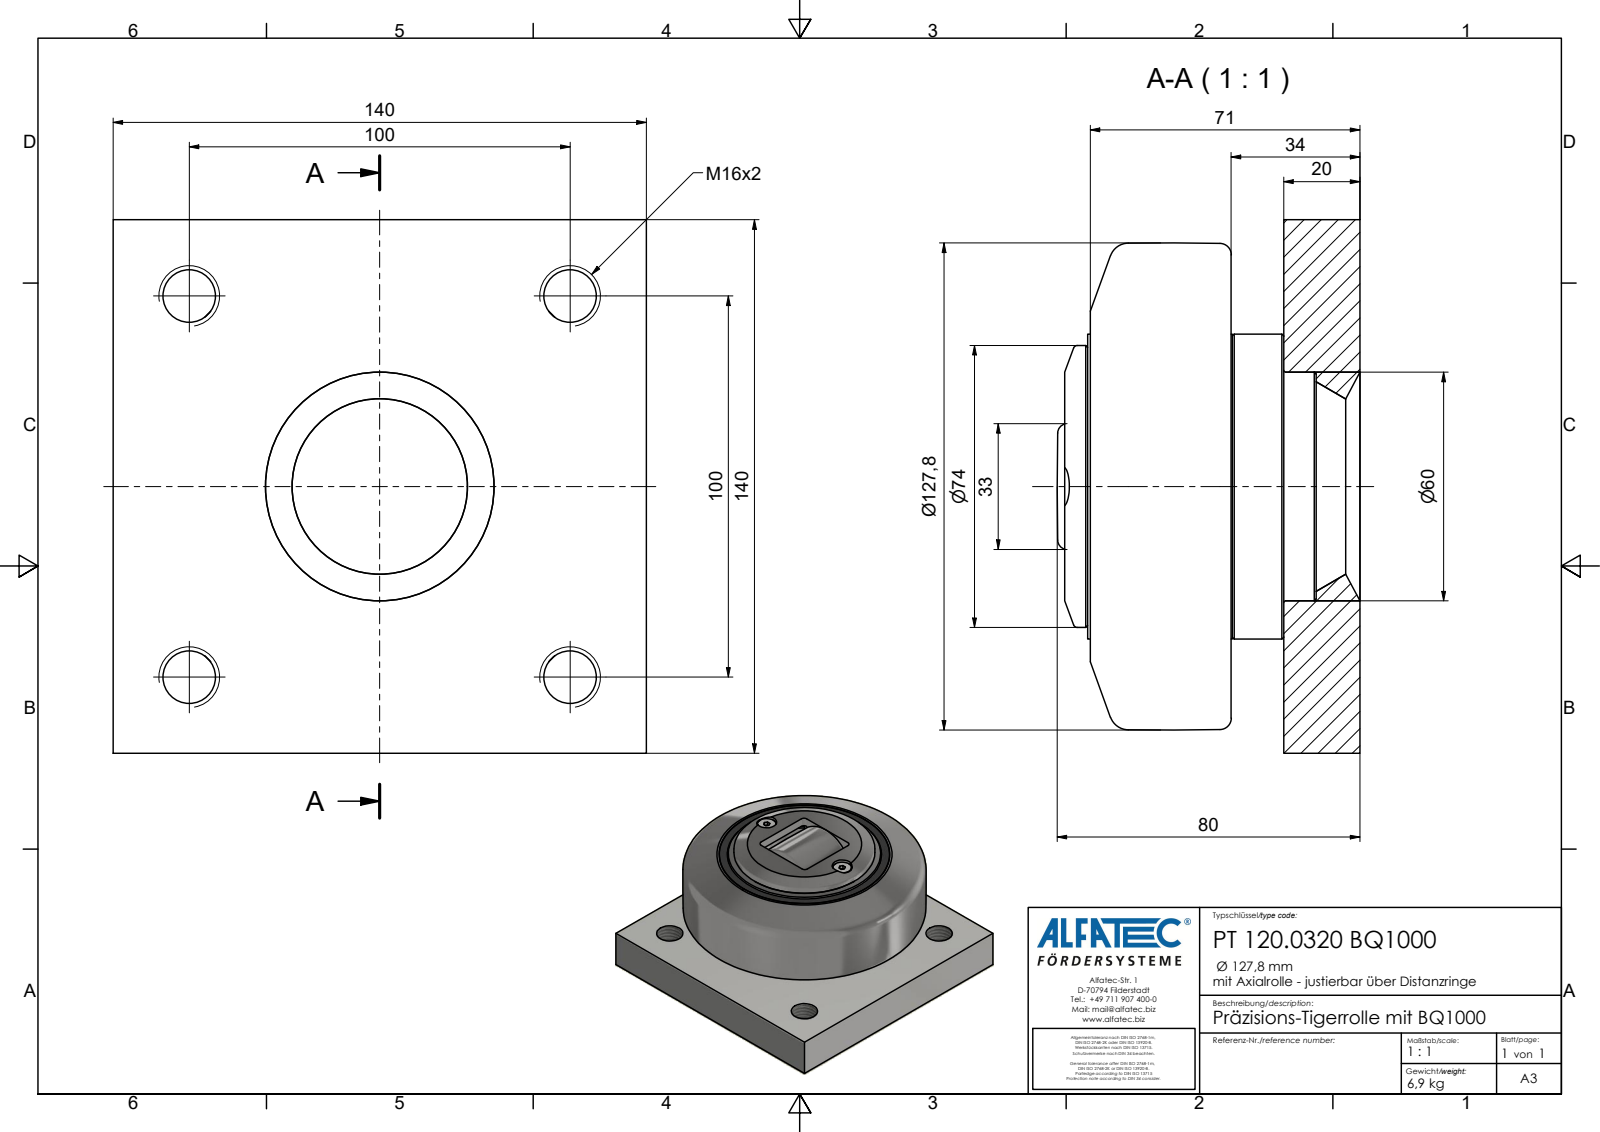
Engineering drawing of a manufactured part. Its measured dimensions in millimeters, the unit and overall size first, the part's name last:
Units: millimetres
Overall size (bounding box): 140 × 140 × 79.5
Round holes (diameter × count): ⌀13.84 ×4, ⌀5.5 ×2, ⌀10.5 ×2, ⌀3 ×1, ⌀26 ×1, ⌀28 ×1, ⌀71.4 ×1, ⌀81 ×1, ⌀87 ×1, ⌀89.5 ×1, ⌀95 ×1
Round bosses / shafts (diameter × count): ⌀9.75 ×2, ⌀5 ×2, ⌀86.8 ×1, ⌀84.5 ×1, ⌀80 ×1, ⌀79 ×1, ⌀74 ×1, ⌀71 ×1
Partial cylindrical surfaces — rounded edges, fillets, slot ends (radius × count): R2 ×4, R19 ×1
Main face-to-face distances: 20, 140, 33.8, 13.8, 71.5, 51.5, 37.7, 30.5, 5.5, 6.5
Hole centre spacings: 54.63, 70.71, 92.65, 100, 28, 141.42, 7.7, 56
Volume: 829 224 mm³ · Surface area: 133 756 mm²
Bodies: 2 solids, 126 faces (52 planar, 45 cylindrical, 29 other)
Part name (STEP PRODUCT): PT 120.0320 BQ1000_Kontur
STEP written by: Autodesk Inventor 2020 (AUTOMOTIVE_DESIGN)
